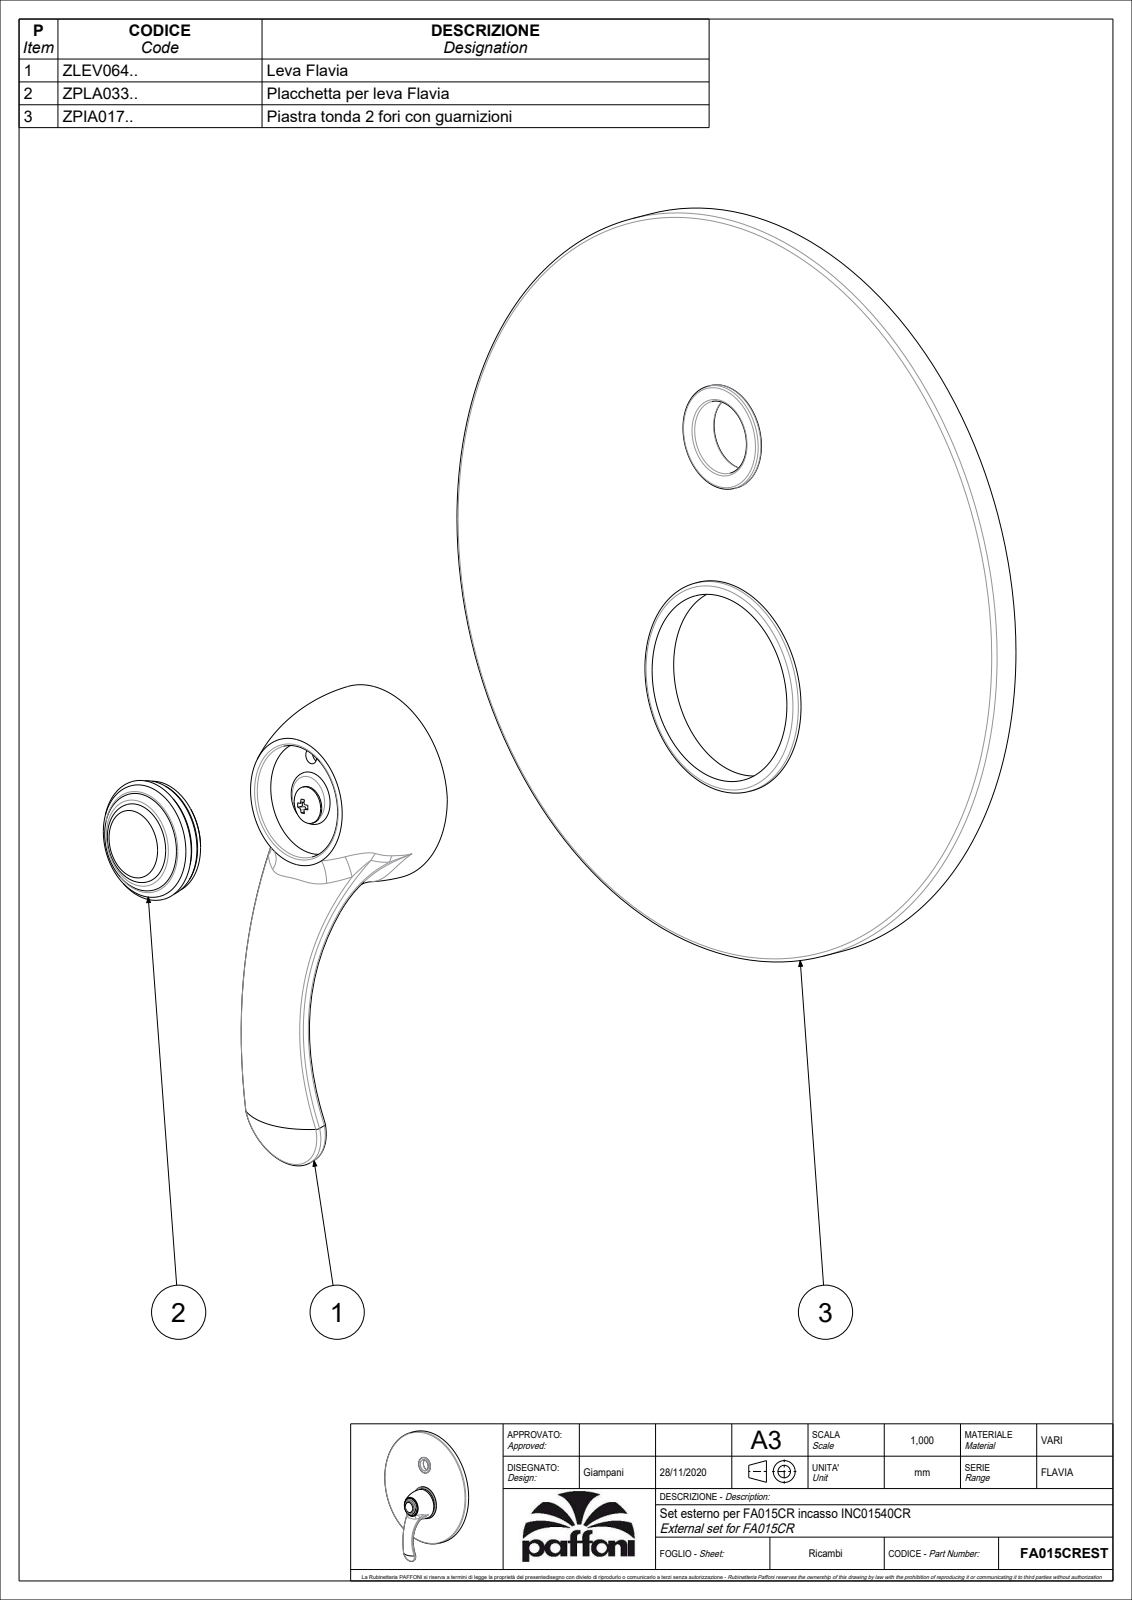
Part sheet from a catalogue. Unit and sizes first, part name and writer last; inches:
Units: inches
Overall size (bounding box): 8.909 × 7.874 × 2.186
Round holes (diameter × count): ⌀0.157 ×1, ⌀0.276 ×1, ⌀0.752 ×1, ⌀1.181 ×1, ⌀1.969 ×1, ⌀5.709 ×1, ⌀7.795 ×1
Round bosses / shafts (diameter × count): ⌀7.874 ×1, ⌀7.677 ×1, ⌀2.224 ×1, ⌀2.165 ×1, ⌀1.177 ×1, ⌀1.063 ×1, ⌀0.988 ×1, ⌀0.925 ×1
Partial cylindrical surfaces — rounded edges, fillets, slot ends (radius × count): R0.02 ×4, R0.059 ×4
Main face-to-face distances: 0.039, 0.315, 0.354, 1.378, 0.098, 0.118, 1.063, 0.079, 1.024, 1.339
Hole centre spacings: 0.049, 0.064, 0.113, 0.399, 0.448, 0.512, 0.654, 1.053
Volume: 10.91 in³ · Surface area: 153.1 in²
Bodies: 2 solids, 259 faces (138 planar, 44 cylindrical, 77 other)
Part name (STEP PRODUCT): FA015CREST
STEP written by: CREO PARAMETRIC BY PTC INC, 2020044 (CONFIG_CONTROL_DESIGN)
